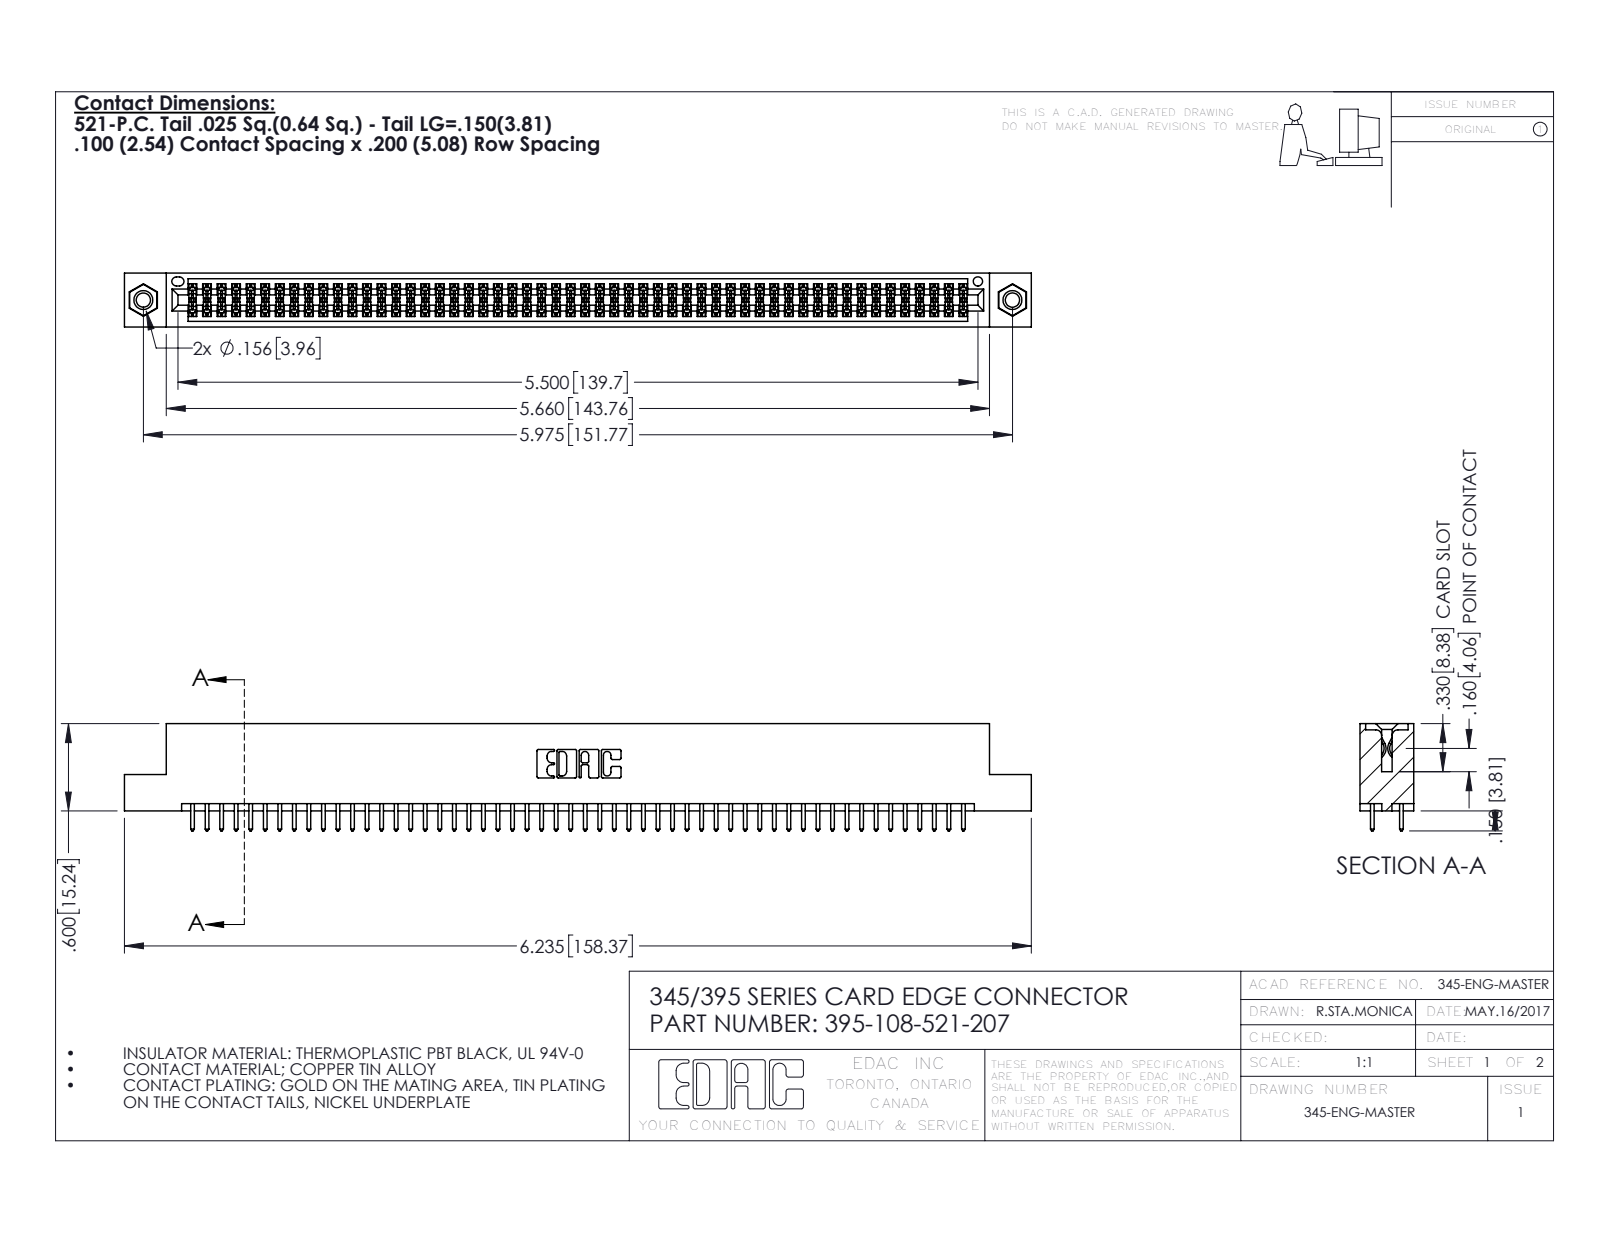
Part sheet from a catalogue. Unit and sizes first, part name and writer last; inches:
Units: inches
Overall size (bounding box): 6.235 × 0.737 × 0.37
Round holes (diameter × count): ⌀0.098 ×2, ⌀0.125 ×2, ⌀0.156 ×2, ⌀0.064 ×1
Round bosses / shafts (diameter × count): ⌀0.155 ×2
Partial cylindrical surfaces — rounded edges, fillets, slot ends (radius × count): R0.006 ×162, R0.01 ×108, R0.01 ×22, R0.007 ×6, R0.031 ×6, R0.026 ×3, R0.014 ×2, R0.019 ×2
Main face-to-face distances: 0.072, 0.298, 0.2, 0.37, 0.098, 0.272, 0.025, 0.225, 0.175, 0.149
Hole centre spacings: 0.27, 5.739, 5.975
Volume: 0.942 in³ · Surface area: 35.33 in²
Bodies: 111 solids, 5586 faces (3676 planar, 1894 cylindrical, 16 other)
Part name (STEP PRODUCT): 345-292-001_345-293-121; 345 Part_Flush Mounting Lugs - 0.156 Dia-TI; 345-250-001_345-250-005-103; 395-108-521-207
STEP written by: SolidWorks 2016 (CONFIG_CONTROL_DESIGN)
